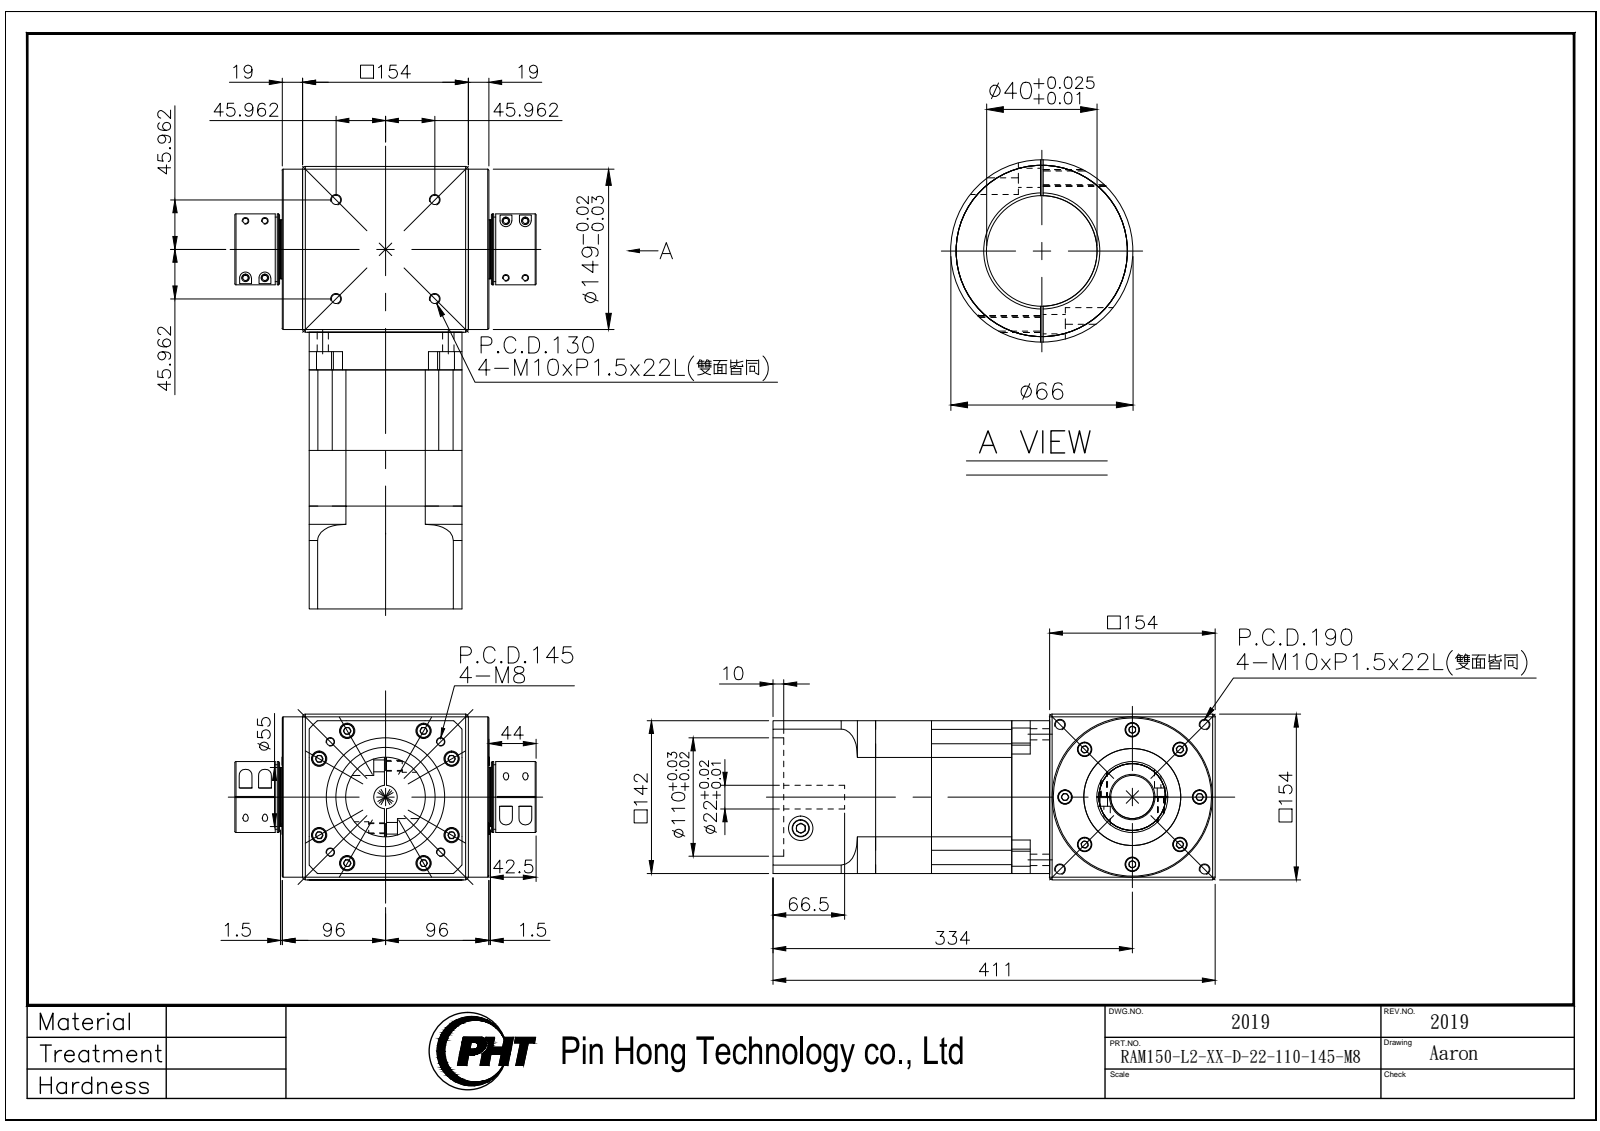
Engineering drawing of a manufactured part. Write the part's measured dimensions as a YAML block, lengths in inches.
part_name: "RAM150-L2-XX-D-22-110-145-M8_2019"
step_written_by: "SolidWorks 2016 (AUTOMOTIVE_DESIGN)"
units: inches
bodies: {solids: 5, faces: 1261, planar: 631, cylindrical: 412, other: 218}
overall_size: [16.181, 11.024, 6.063]
volume: 527.3
surface_area: 992.7
round_holes:
  - {diameter: 0.335, count: 12}
  - {diameter: 0.354, count: 8}
  - {diameter: 0.433, count: 8}
  - {diameter: 0.551, count: 8}
  - {diameter: 0.689, count: 8}
  - {diameter: 0.276, count: 6}
  - {diameter: 0.268, count: 4}
  - {diameter: 0.413, count: 4}
  - {diameter: 0.886, count: 2}
  - {diameter: 0.866, count: 1}
  - {diameter: 1.575, count: 1}
  - {diameter: 1.732, count: 1}
round_bosses_or_shafts:
  - {diameter: 0.63, count: 12}
  - {diameter: 0.512, count: 8}
  - {diameter: 0.413, count: 8}
  - {diameter: 0.394, count: 8}
  - {diameter: 0.236, count: 8}
  - {diameter: 5.866, count: 1}
  - {diameter: 5.118, count: 1}
  - {diameter: 3.543, count: 1}
partial_cylinders:
  - {radius: 0.139, count: 8}
  - {radius: 0.217, count: 8}
  - {radius: 0.394, count: 4}
  - {radius: 3.15, count: 1}
  - {radius: 3.74, count: 1}
  - {radius: 4.228, count: 1}
face_to_face_distances: [0.236, 5.827, 6.063, 5.591, 2.039, 4.98, 2.941, 1.378, 6.358, 4.319]
hole_center_spacings: [2.795, 0.737, 0.74, 0.908, 1.883, 2.651, 3.265, 3.44]
